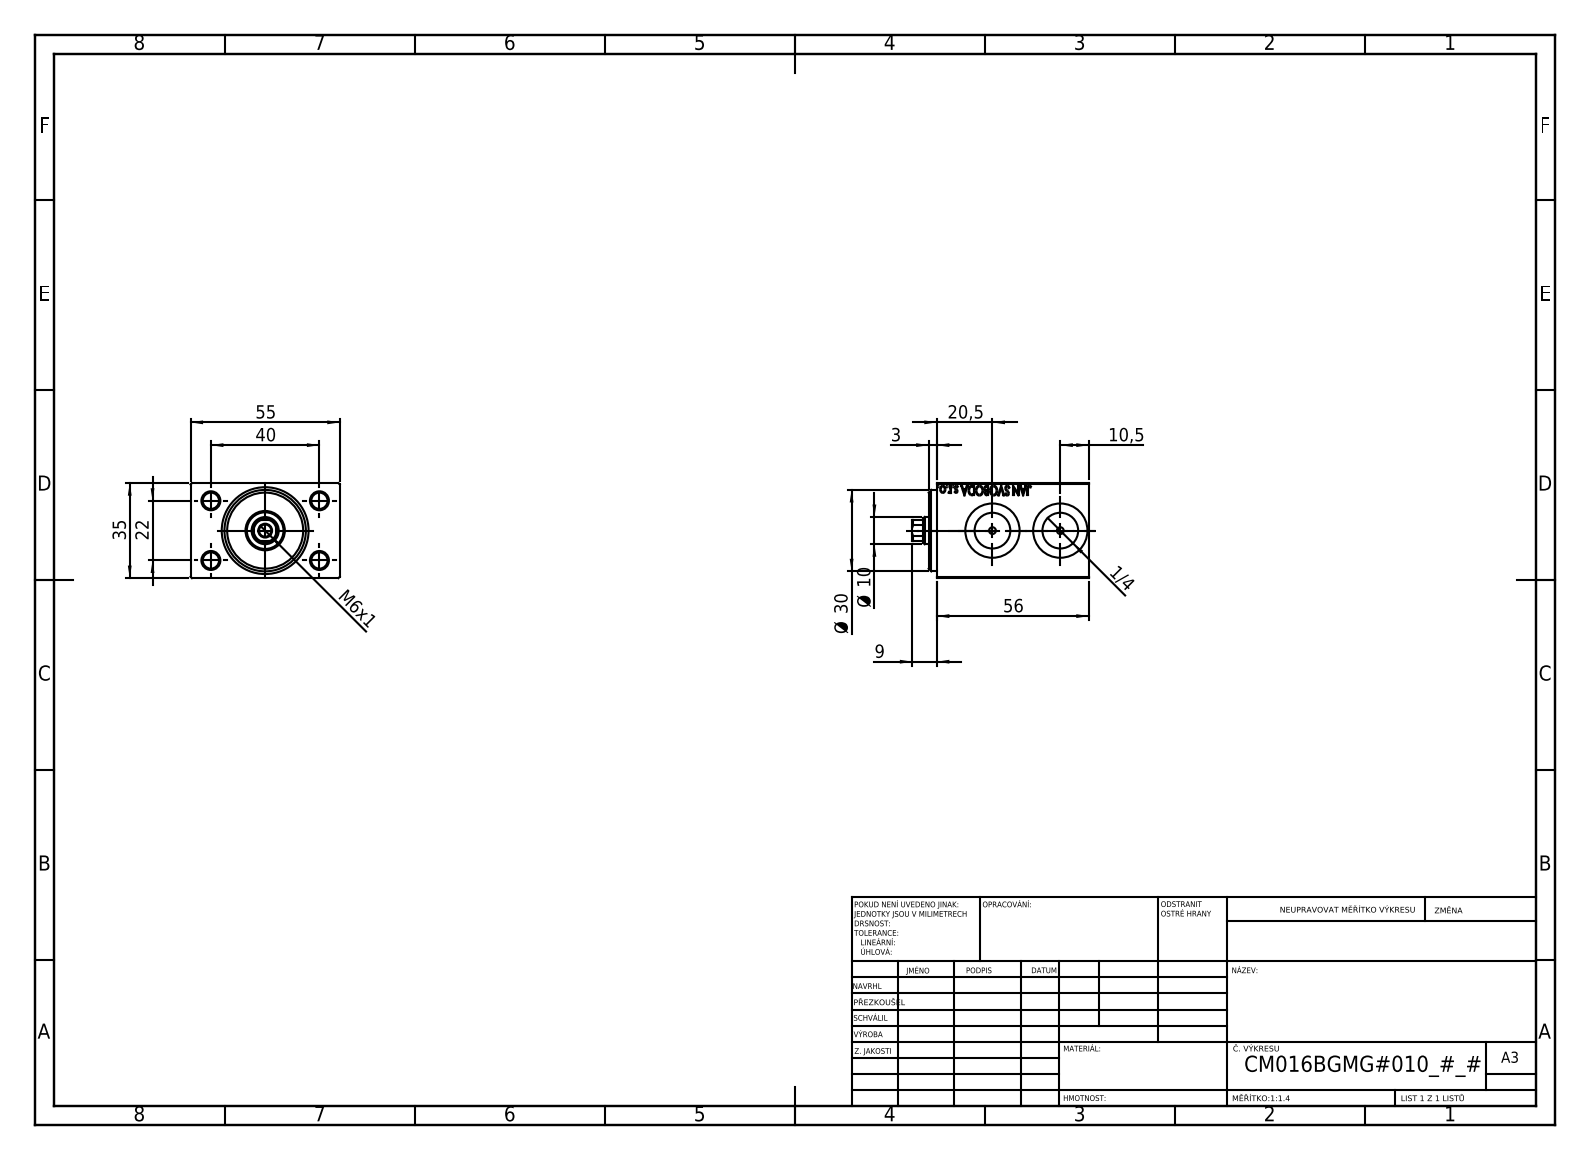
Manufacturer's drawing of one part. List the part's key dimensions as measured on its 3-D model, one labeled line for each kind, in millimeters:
Part name (STEP PRODUCT): V450CM_VC_B; V450CM_B_VCP; V450CM_B_Body
STEP written by: SolidWorks 2019 (CONFIG_CONTROL_DESIGN)
Units: millimetres
Bodies: 3 solids, 881 faces (401 planar, 54 cylindrical, 426 other)
Overall size (bounding box): 65 × 55 × 35
Volume: 102 523 mm³ · Surface area: 25 047 mm²
Round holes (diameter × count): ⌀6 ×4, ⌀2.5 ×2, ⌀13.16 ×2, ⌀20 ×2, ⌀4.5 ×1, ⌀10 ×1, ⌀13.5 ×1, ⌀14.5 ×1, ⌀16 ×1, ⌀18 ×1, ⌀30 ×1
Partial cylindrical surfaces — rounded edges, fillets, slot ends (radius × count): R4.5 ×1
Main face-to-face distances: 35, 5, 51, 55, 56, 8, 3, 59, 54, 46
Hole centre spacings: 22.83, 22, 40, 45.65, 25
